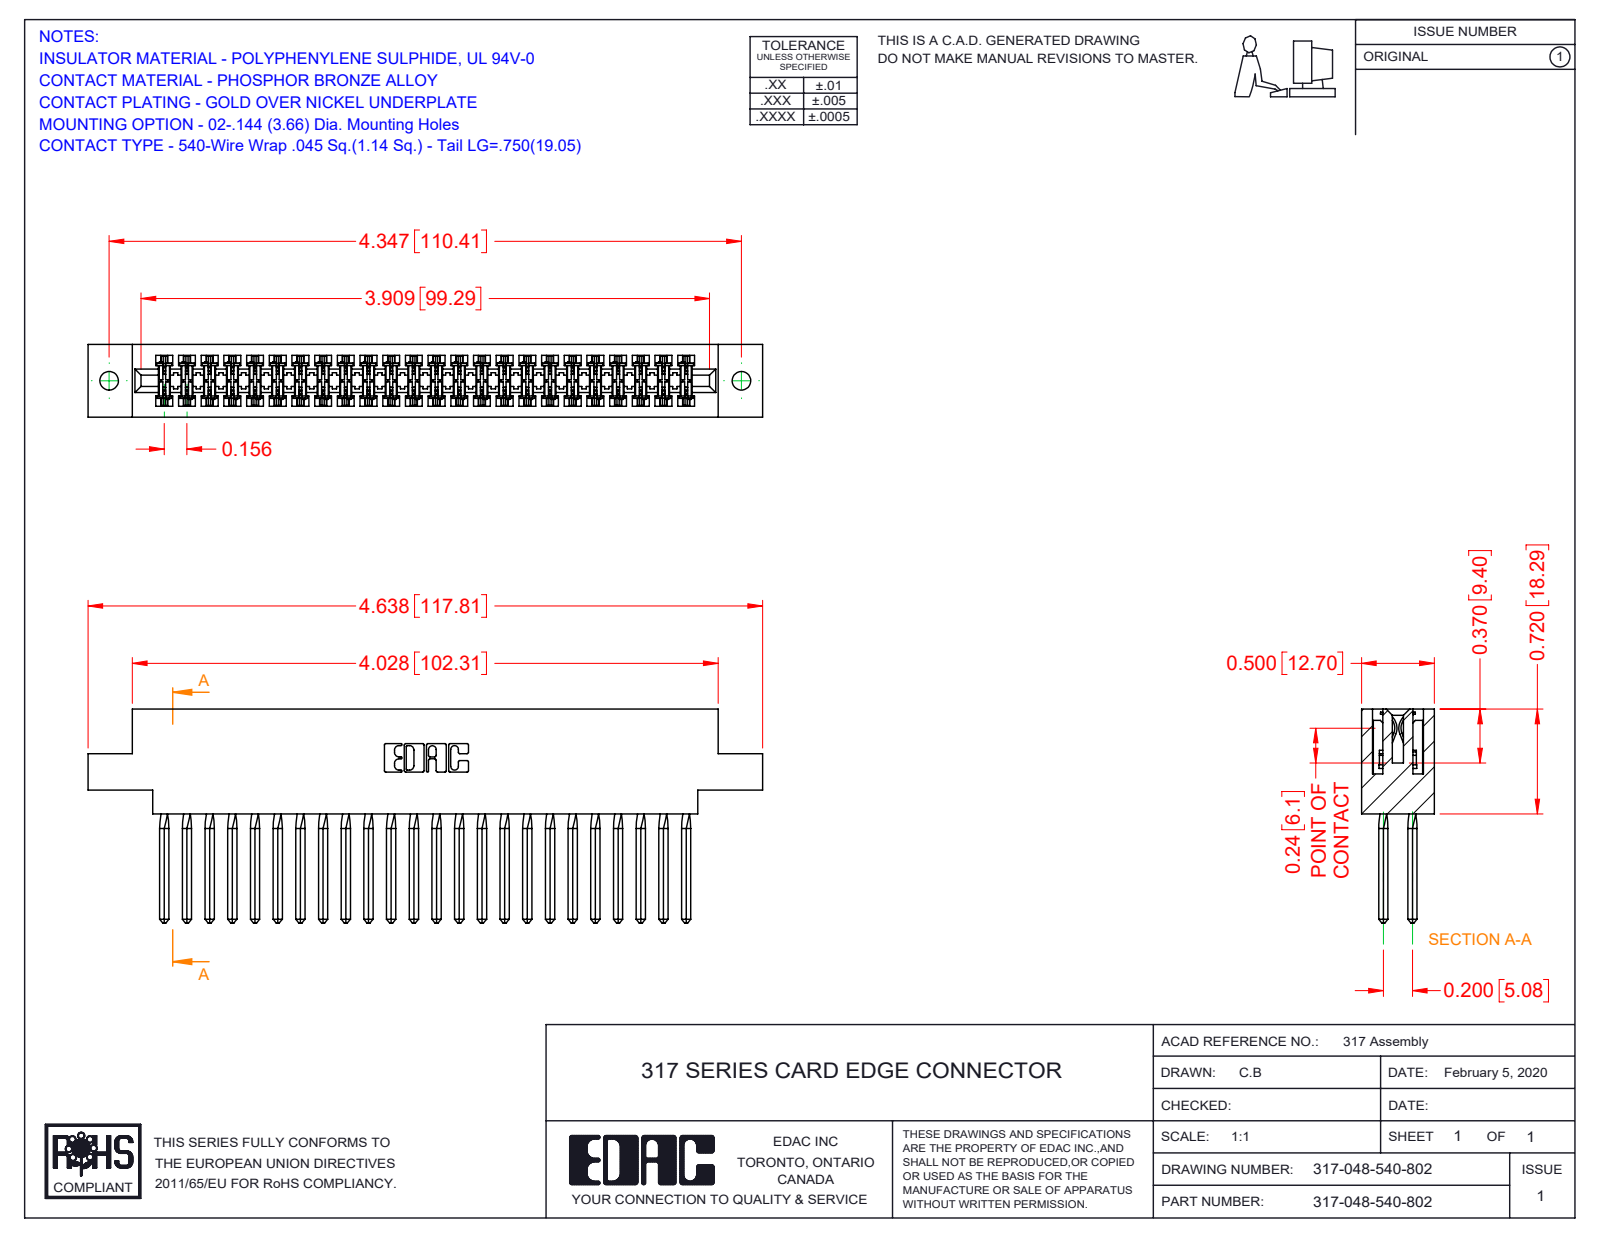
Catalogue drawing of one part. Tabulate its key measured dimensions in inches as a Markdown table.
| quantity | value |
| --- | --- |
| part name | 317-290-001_540; 317-048-540-802; 317 Part_.144 Dia |
| STEP written by | SolidWorks 2016 (CONFIG_CONTROL_DESIGN) |
| units | inches |
| bodies | 49 solids, 4374 faces (3562 planar, 620 cylindrical, 192 other) |
| overall size | 4.638 × 1.47 × 0.5 |
| volume | 1.167 in³ |
| surface area | 42.74 in² |
| round holes (diameter × count) | 0.128 × 2 |
| partial cylindrical surfaces (radius × count) | 0.015 × 96, 0.01 × 22, 0.007 × 6, 0.031 × 6, 0.026 × 3, 0.095 × 2, 0.1 × 2, 0.11 × 2 |
| main face-to-face distances | 0.5, 0.075, 0.425, 0.35, 0.11, 0.195, 0.094, 0.72, 0.2, 0.115 |
| hole center spacings | 4.347 |
